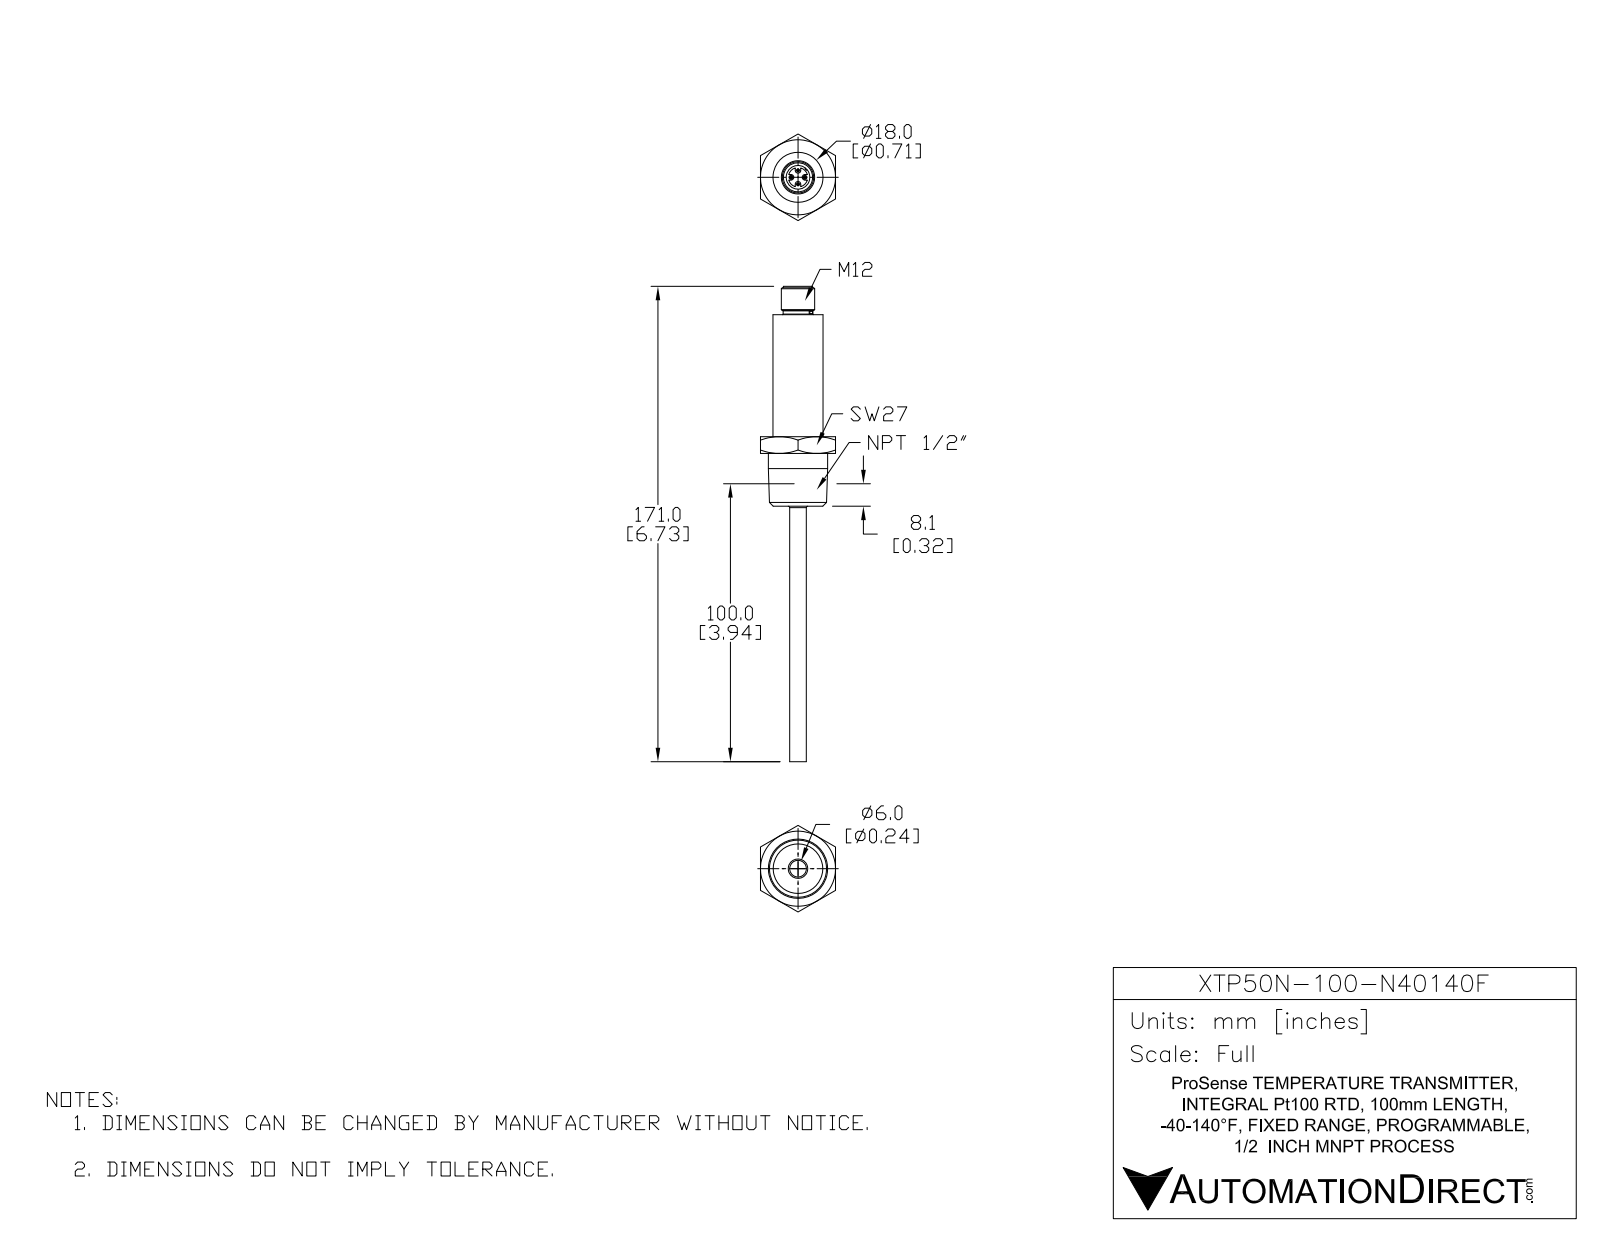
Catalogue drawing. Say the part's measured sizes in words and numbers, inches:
The part is named "XTP50N-100-N40140F". Its 3-D file was written by "SolidWorks 2015 (AUTOMOTIVE_DESIGN)". It is 1 solid with 117 faces: 43 planar, 34 cylindrical and 40 other. Overall it measures 6.732 by 1.228 by 1.063 inches. Its volume is 1.485 cubic inches and its surface area 12.73 square inches. Round holes: 1 of diameter 0.157, 1 of diameter 0.335. Round bosses or shafts: 4 of diameter 0.04, 1 of diameter 0.84, 1 of diameter 0.709, 1 of diameter 0.472, 1 of diameter 0.421, 1 of diameter 0.413, 1 of diameter 0.236. Partial cylindrical surfaces (rounded edges, fillets, slot ends): 4 of radius 0.039, 1 of radius 0.138, 1 of radius 0.167. The main face-to-face distances are 1.063, 0.984, 0.748, 0.236, 2.713, 1.965, 1.728, 3.114, 2.366, 2.13.
